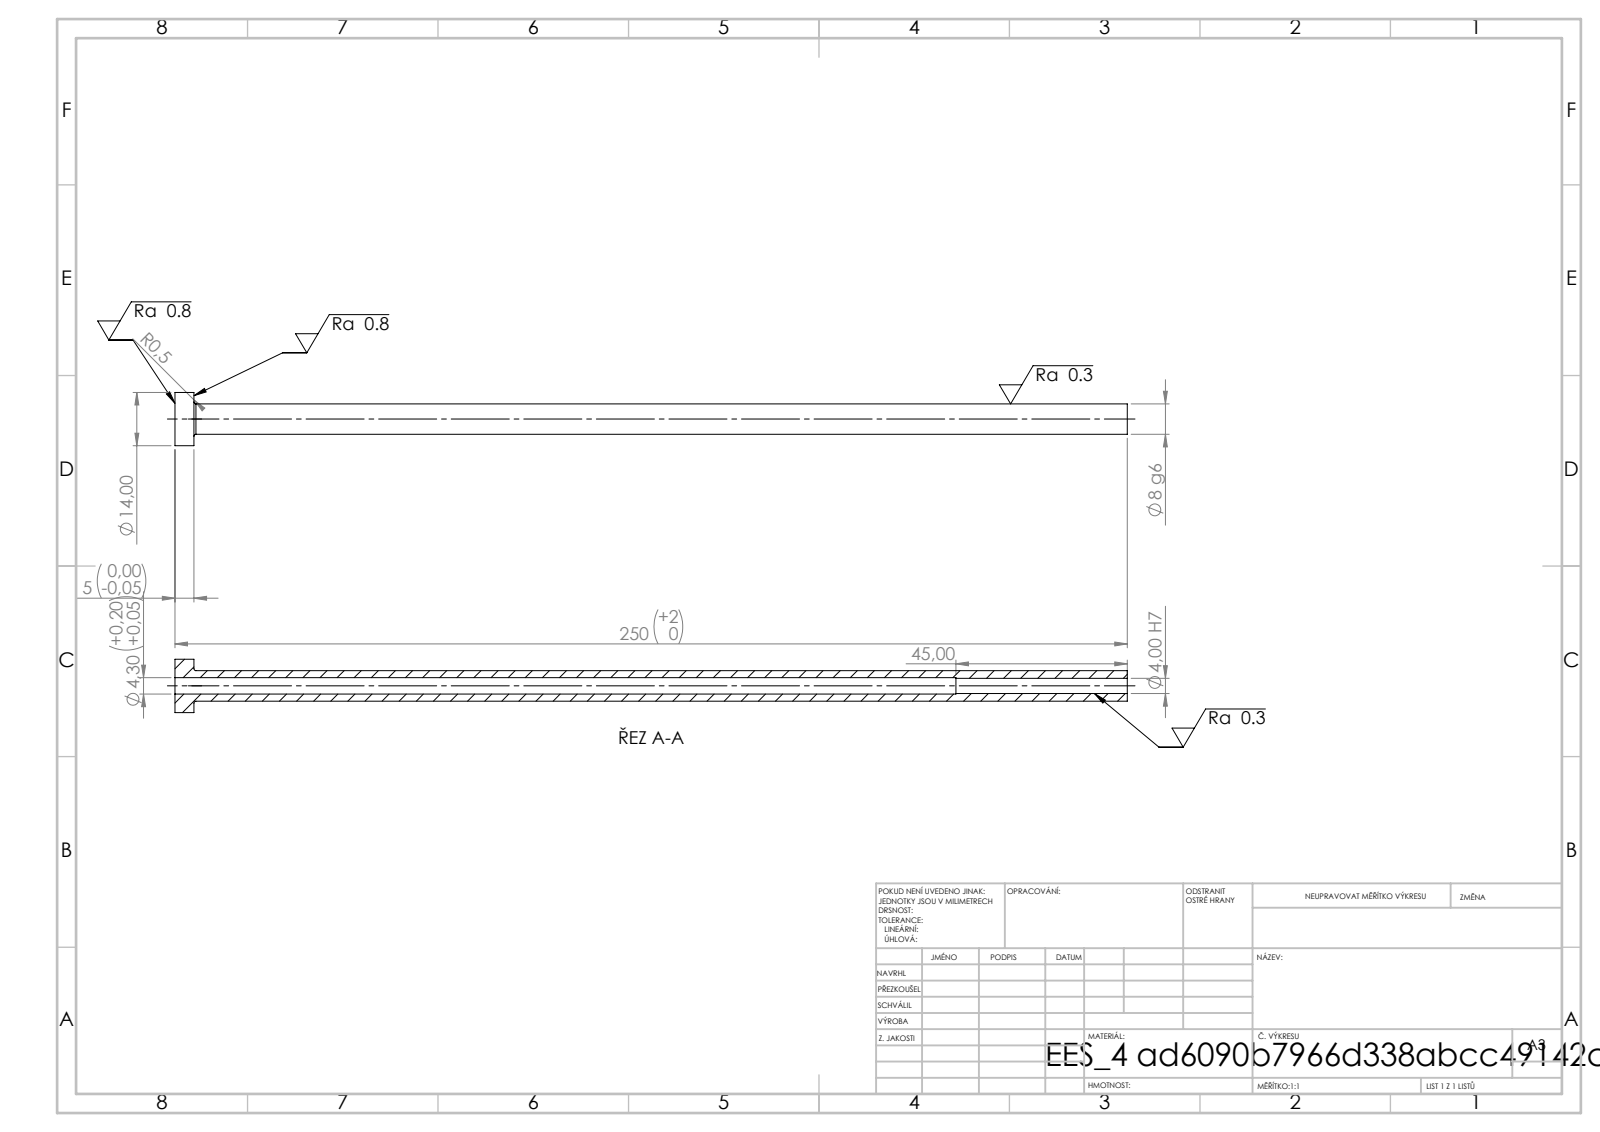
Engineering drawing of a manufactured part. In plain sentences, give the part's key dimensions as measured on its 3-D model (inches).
Its 3-D file was written by "SolidWorks 2019 (CONFIG_CONTROL_DESIGN)". It is 1 solid with 14 faces: 4 planar, 8 cylindrical and 2 other. Overall it measures 9.843 by 0.551 by 0.551 inches. Its volume is 0.582 cubic inches and its surface area 15.48 square inches. Round holes: 1 of diameter 0.157, 1 of diameter 0.169. Round bosses or shafts: 1 of diameter 0.551, 1 of diameter 0.315. The main face-to-face distances are 0.197, 9.843, 9.646, 8.071, 7.874, 1.772.
